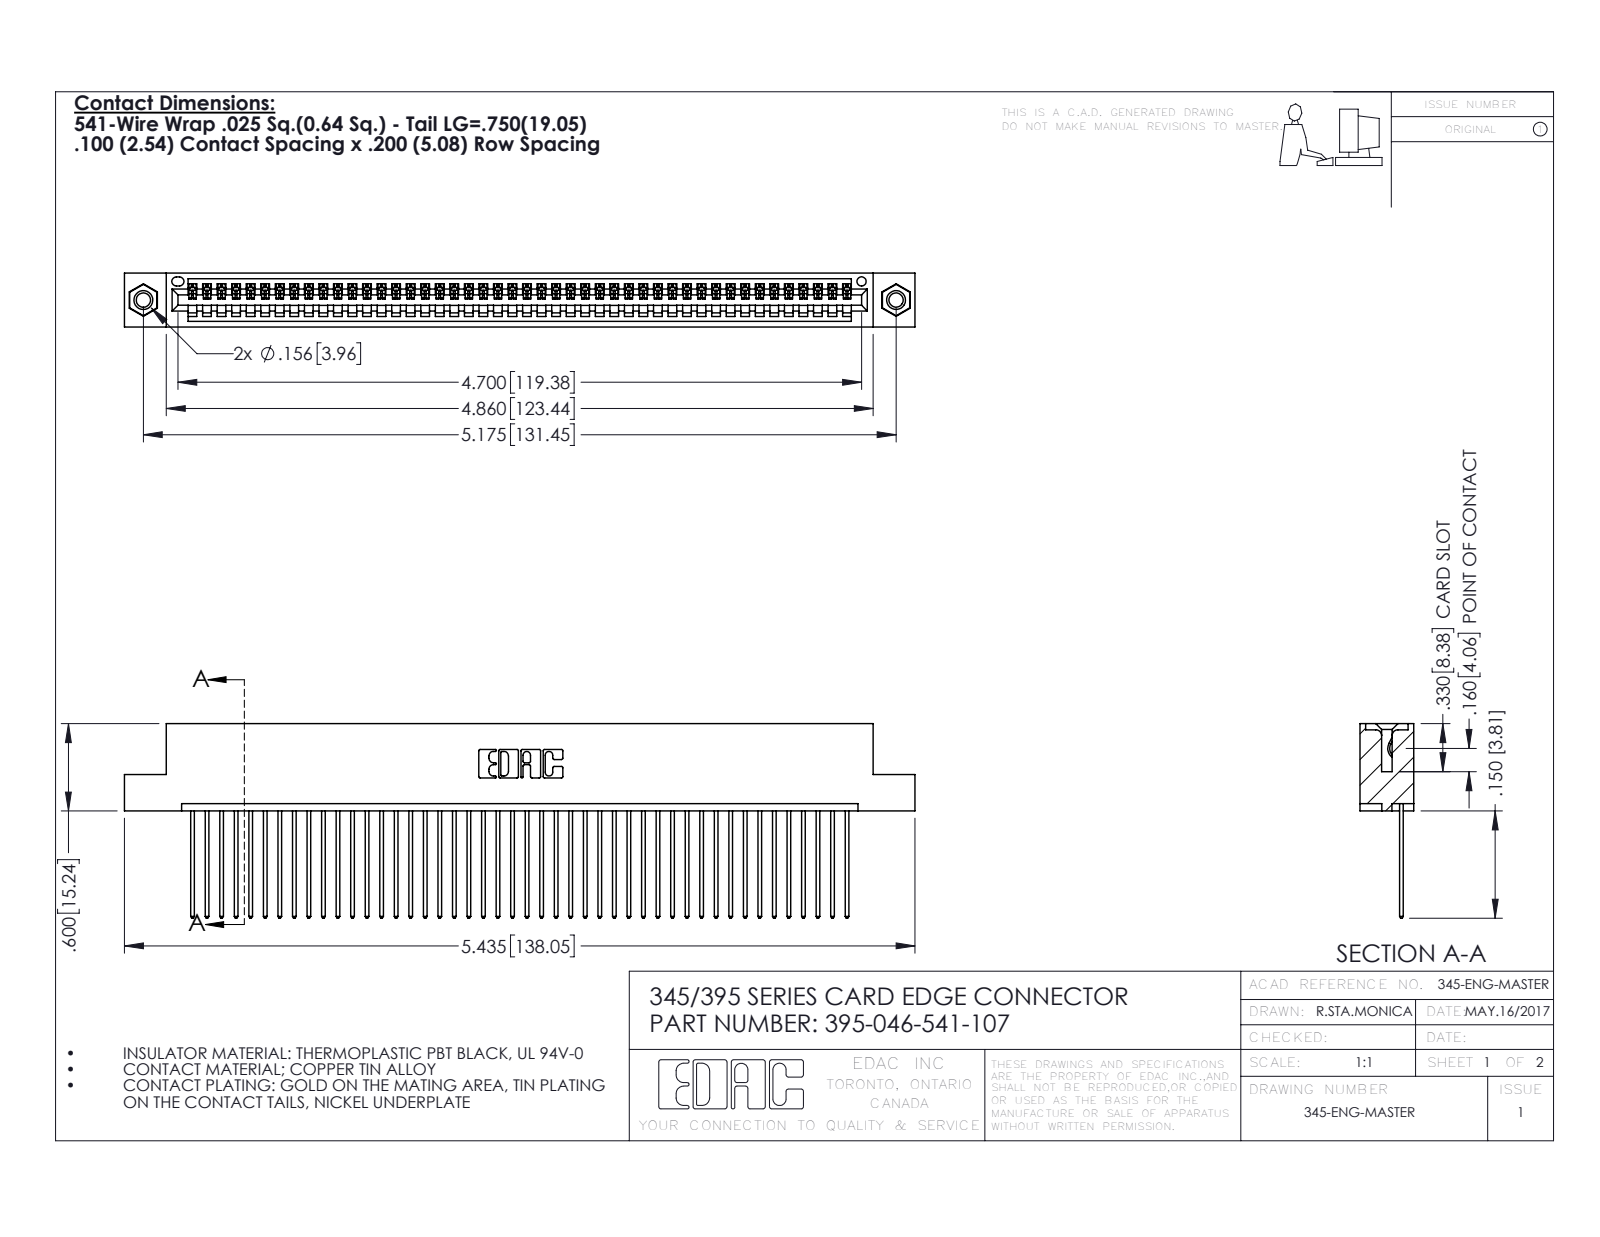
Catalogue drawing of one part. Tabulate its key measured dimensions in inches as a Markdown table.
| quantity | value |
| --- | --- |
| part name | 345-292-001_345-293-141; 345-250-001_345-250-005-103; 345 Part_Flush Mounting Lugs - 0.156 Dia-TI; 395-046-541-107 |
| STEP written by | SolidWorks 2016 (CONFIG_CONTROL_DESIGN) |
| units | inches |
| bodies | 49 solids, 2854 faces (1952 planar, 886 cylindrical, 16 other) |
| overall size | 5.435 × 1.337 × 0.37 |
| volume | 0.811 in³ |
| surface area | 28.88 in² |
| round holes (diameter × count) | 0.098 × 2, 0.125 × 2, 0.156 × 2, 0.064 × 1 |
| round bosses / shafts (diameter × count) | 0.155 × 2 |
| partial cylindrical surfaces (radius × count) | 0.006 × 92, 0.01 × 92, 0.01 × 22, 0.007 × 6, 0.031 × 6, 0.026 × 3, 0.031 × 2, 0.04 × 2 |
| main face-to-face distances | 0.072, 0.298, 0.098, 0.272, 0.025, 0.37, 0.2, 0.225, 0.149, 0.072 |
| hole center spacings | 0.27, 4.939, 5.175 |
